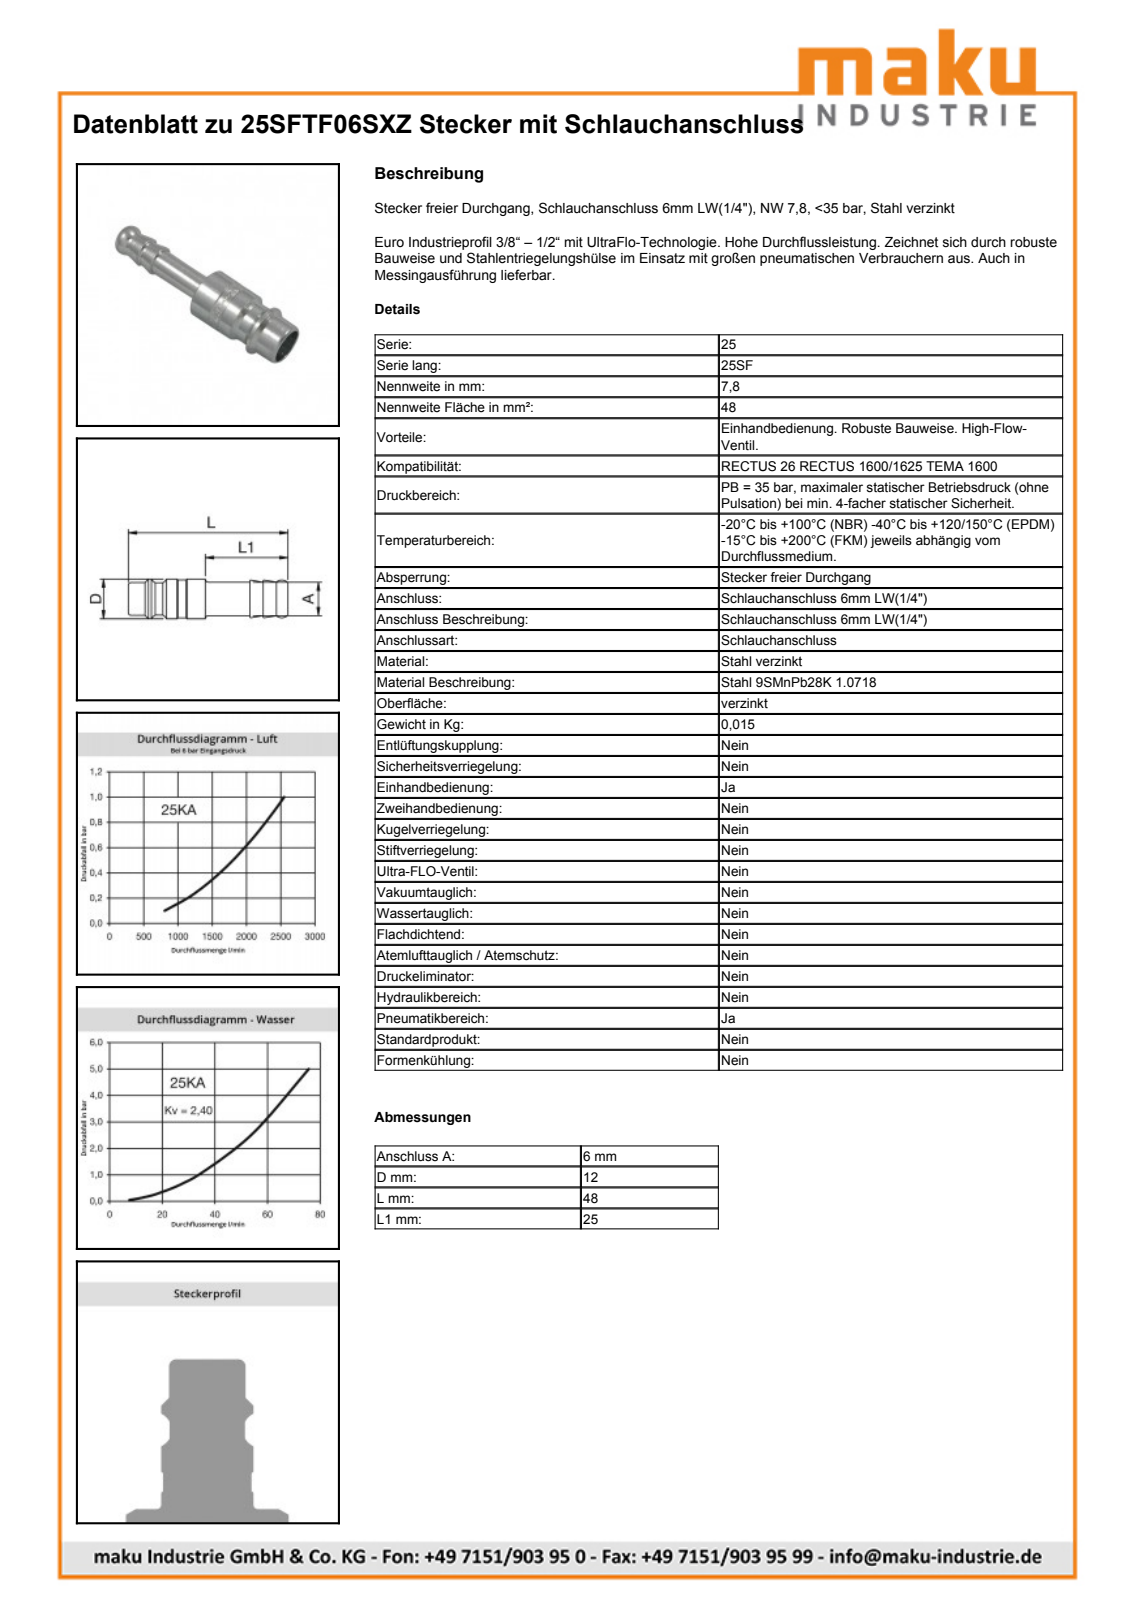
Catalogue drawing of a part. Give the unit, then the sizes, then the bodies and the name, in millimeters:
Units: millimetres
Overall size (bounding box): 48.3 × 12 × 12
Round holes (diameter × count): ⌀4.1 ×1, ⌀7.85 ×1
Round bosses / shafts (diameter × count): ⌀12 ×1, ⌀9.9 ×1, ⌀9.75 ×1, ⌀6.1 ×1
Main face-to-face distances: 25, 13.5, 11.5, 23.3, 36.8, 48.3
Volume: 1 747 mm³ · Surface area: 2 380 mm²
Bodies: 1 solid, 24 faces (4 planar, 7 cylindrical, 13 other)
Part name (STEP PRODUCT): D103591
STEP written by: Autodesk Inventor 2011 (AUTOMOTIVE_DESIGN)
